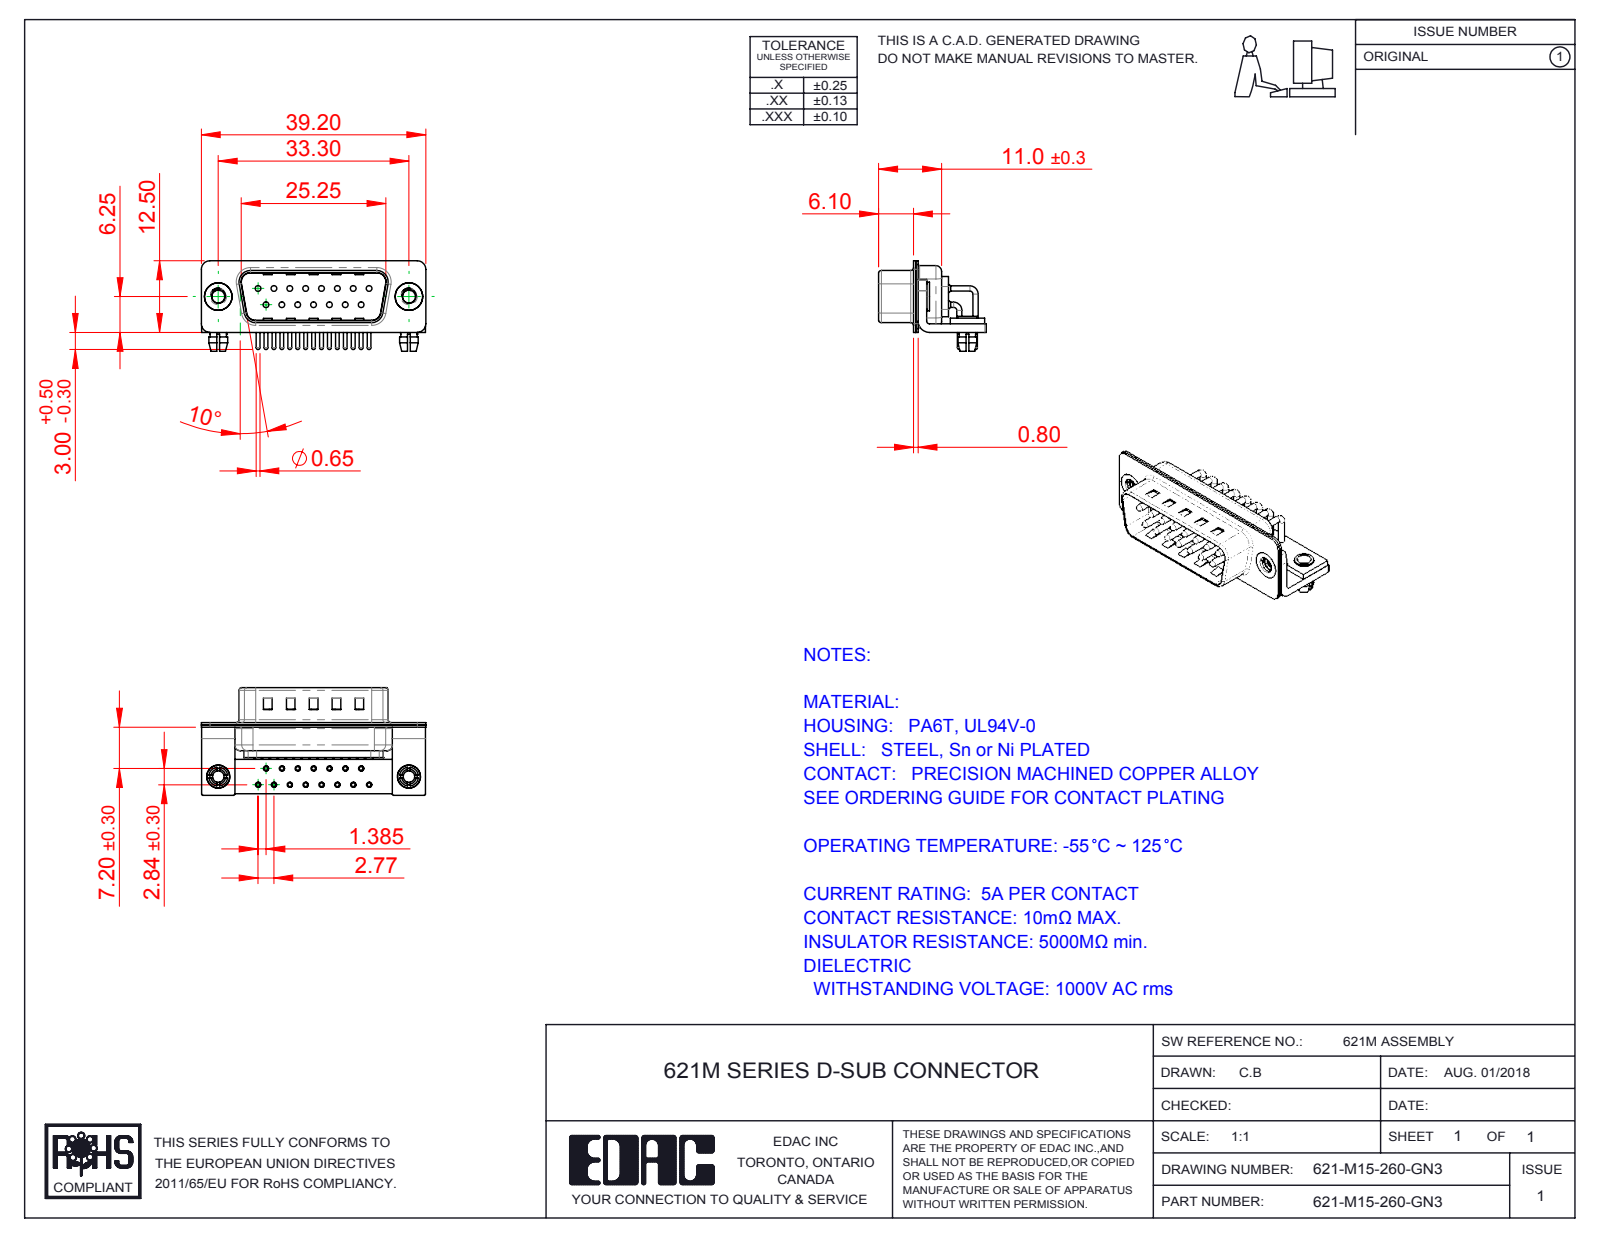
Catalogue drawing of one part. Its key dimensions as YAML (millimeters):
part_name: "621M Contact Row 2; 621M Stabilizer Board_15 Contacts; 621M Contact Row 1; 621-M15-260-GN3 (+6 more)"
step_written_by: "SolidWorks 2016 (CONFIG_CONTROL_DESIGN)"
units: millimeters
bodies: {solids: 25, faces: 2162, planar: 1173, cylindrical: 757, other: 232}
overall_size: [39.2, 18.8, 15.8]
volume: 2417
surface_area: 6593
round_holes:
  - {diameter: 2, count: 17}
  - {diameter: 0.9, count: 15}
  - {diameter: 1, count: 15}
  - {diameter: 1.7, count: 15}
  - {diameter: 2.26, count: 2}
  - {diameter: 2.5, count: 2}
  - {diameter: 3.2, count: 2}
  - {diameter: 4, count: 2}
  - {diameter: 4.8, count: 2}
round_bosses_or_shafts:
  - {diameter: 0.9, count: 22}
  - {diameter: 1.5, count: 15}
  - {diameter: 0.65, count: 15}
  - {diameter: 5, count: 2}
  - {diameter: 4.9, count: 2}
  - {diameter: 4, count: 2}
  - {diameter: 3.4, count: 2}
  - {diameter: 3.3, count: 2}
partial_cylinders:
  - {radius: 0.25, count: 16}
  - {radius: 1.5, count: 16}
  - {radius: 1.01, count: 15}
  - {radius: 2, count: 13}
  - {radius: 0.5, count: 9}
  - {radius: 1.6, count: 8}
  - {radius: 0.6, count: 4}
  - {radius: 0.65, count: 4}
face_to_face_distances: [0.4, 0.85, 1.5, 0.8, 1.25, 10.4, 9.55, 1, 2.1, 1.9]
hole_center_spacings: [3.16, 2.77, 5.54, 8.31, 11.08, 5.03, 5.04, 7.48]
